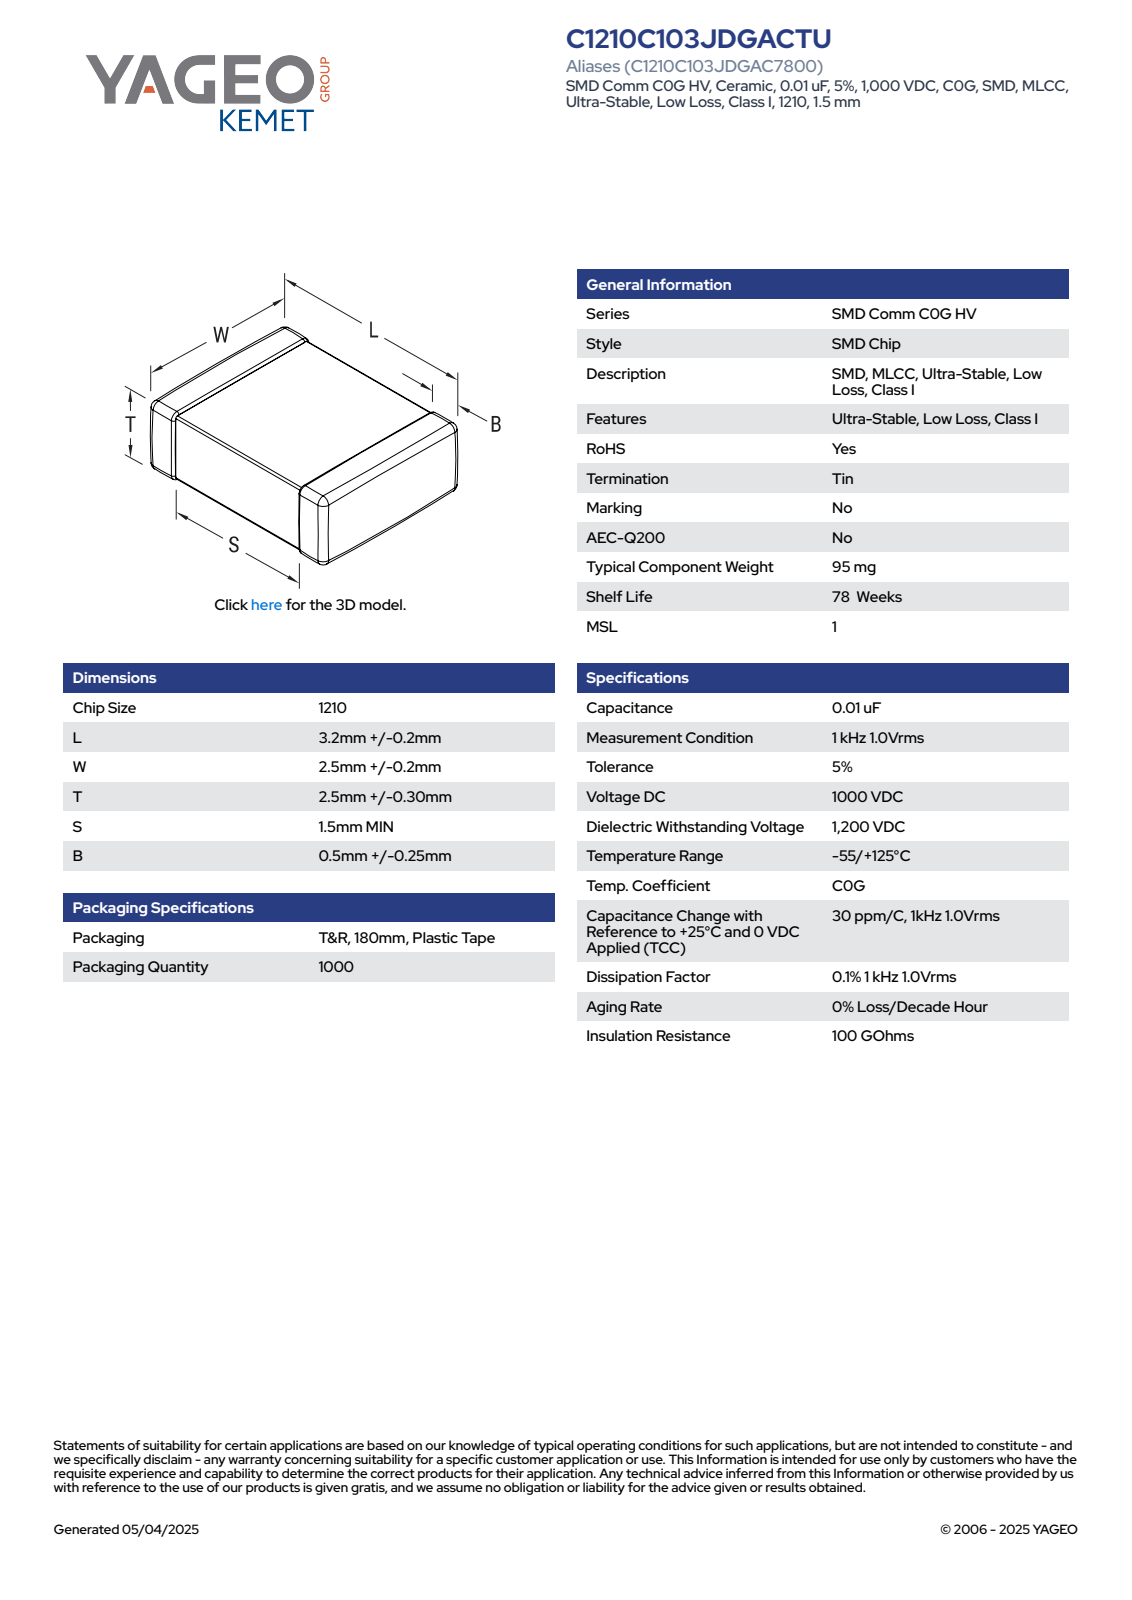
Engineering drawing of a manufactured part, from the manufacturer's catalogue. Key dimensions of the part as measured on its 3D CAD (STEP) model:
Part name (STEP PRODUCT): CCS_CCSTD_1210_L3.4W2.7T2.8B0.5
STEP written by: SolidWorks 2021 (AUTOMOTIVE_DESIGN)
Units: millimetres
Bodies: 4 solids, 125 faces (71 planar, 38 cylindrical, 16 other)
Overall size (bounding box): 3.4 × 2.8 × 2.7
Volume: 25 mm³ · Surface area: 52 mm²
Main face-to-face distances: 3.4, 2.64, 2.74, 2.58, 2.68, 2.7, 2.8, 2.75, 2.69, 0.4
